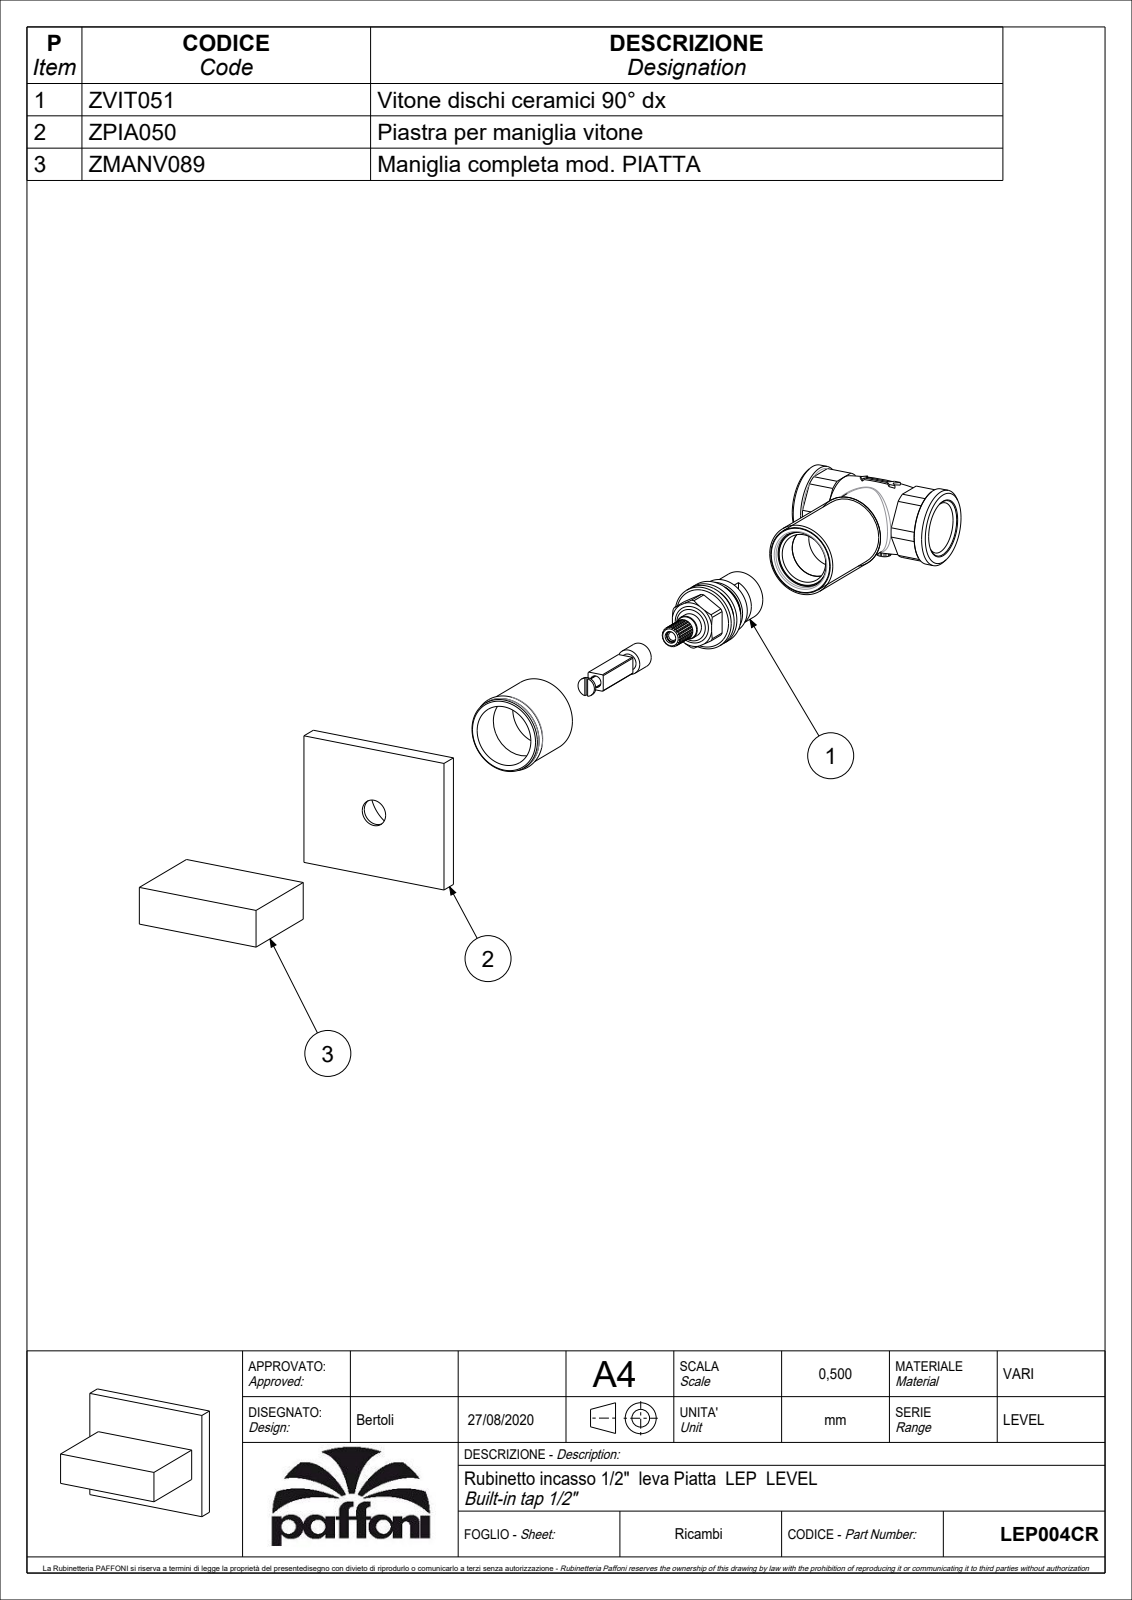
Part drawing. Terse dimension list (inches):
name: LEP004CR
written by: CREO PARAMETRIC BY PTC INC, 2020044 (CONFIG_CONTROL_DESIGN)
unit: in
bodies: 1 solid, 107 faces (57 planar, 34 cylindrical, 16 other)
size: 2.362 × 1.969 × 1.685
volume: 2.205 in³; area: 27.23 in²
holes: 1× ⌀0.165, 1× ⌀0.177, 1× ⌀0.335, 1× ⌀0.378, 1× ⌀0.386, 1× ⌀0.394, 1× ⌀0.492, 1× ⌀1.122, 1× ⌀1.85
bosses: 1× ⌀1.181, 1× ⌀0.488, 1× ⌀0.276, 1× ⌀0.248, 1× ⌀0.157, 1× ⌀0.15
rounds: 1× R0.069
face distances: 0.571, 0.059, 0.217, 0.276, 1.969, 0.699, 1.27, 1.469, 1.685, 1.409
